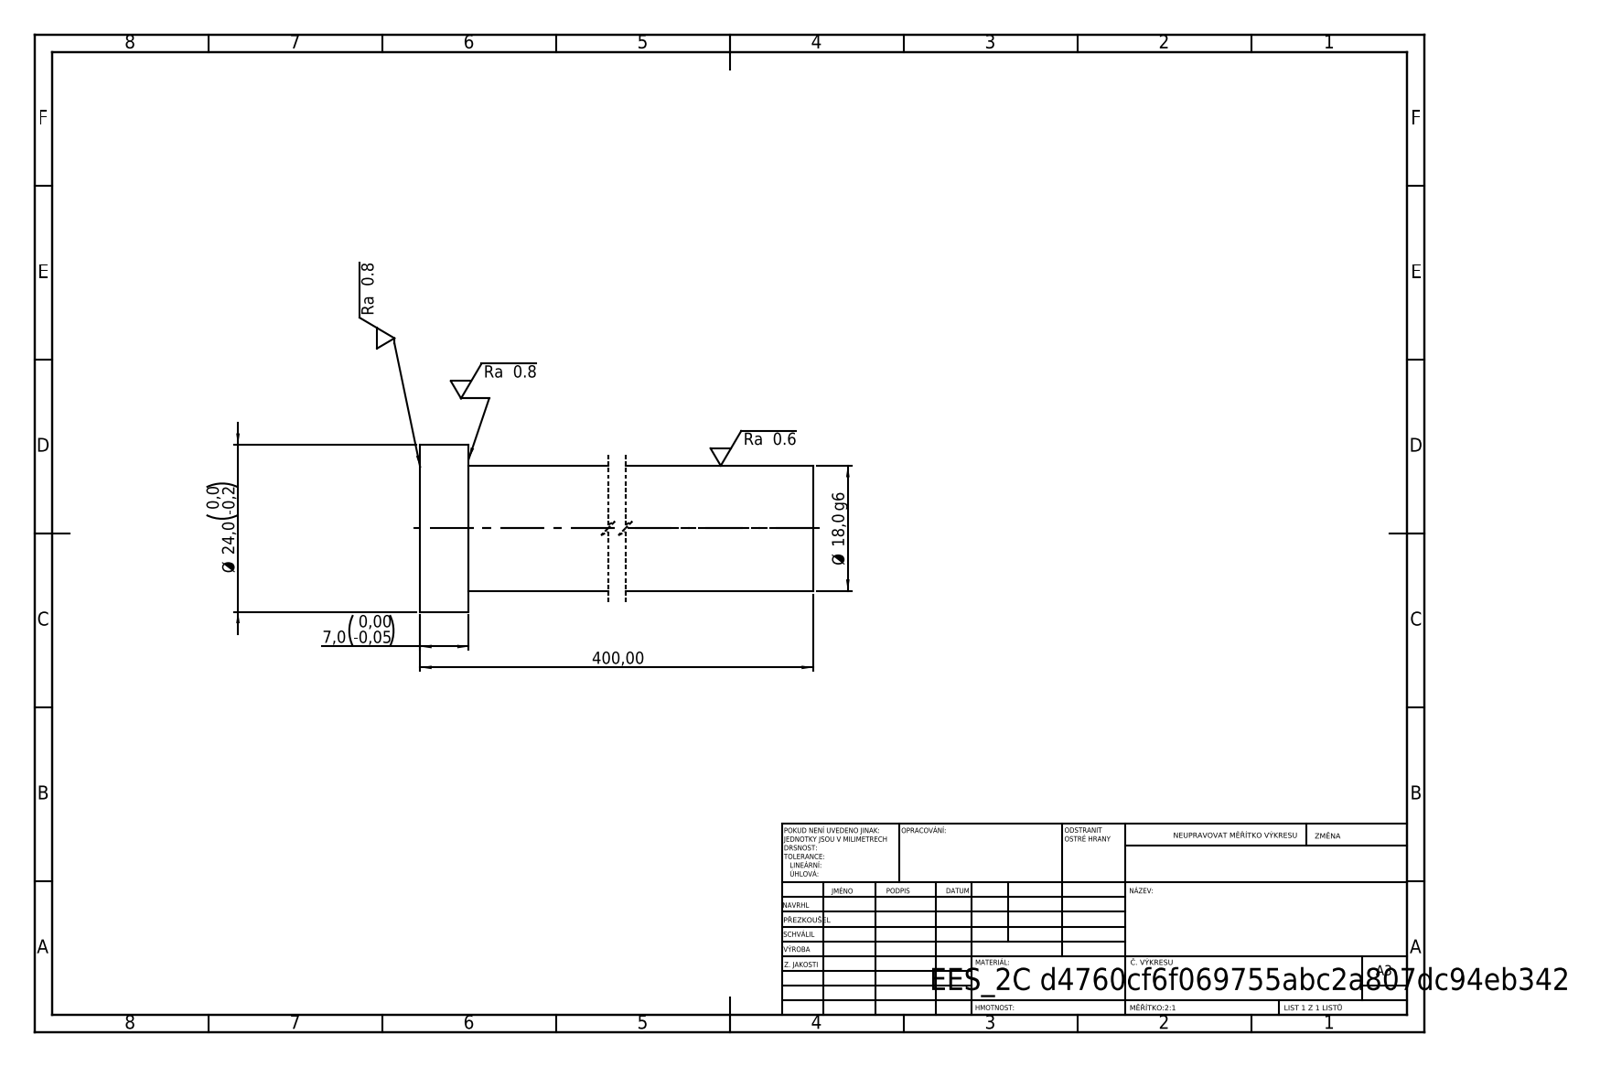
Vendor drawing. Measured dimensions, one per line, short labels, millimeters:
written by: SolidWorks 2019 (CONFIG_CONTROL_DESIGN)
unit: mm
bodies: 1 solid, 7 faces (3 planar, 4 cylindrical, 0 other)
size: 400 × 24 × 24
volume: 103 173 mm³; area: 23 656 mm²
bosses: 1× ⌀24, 1× ⌀18
face distances: 400, 7, 393
